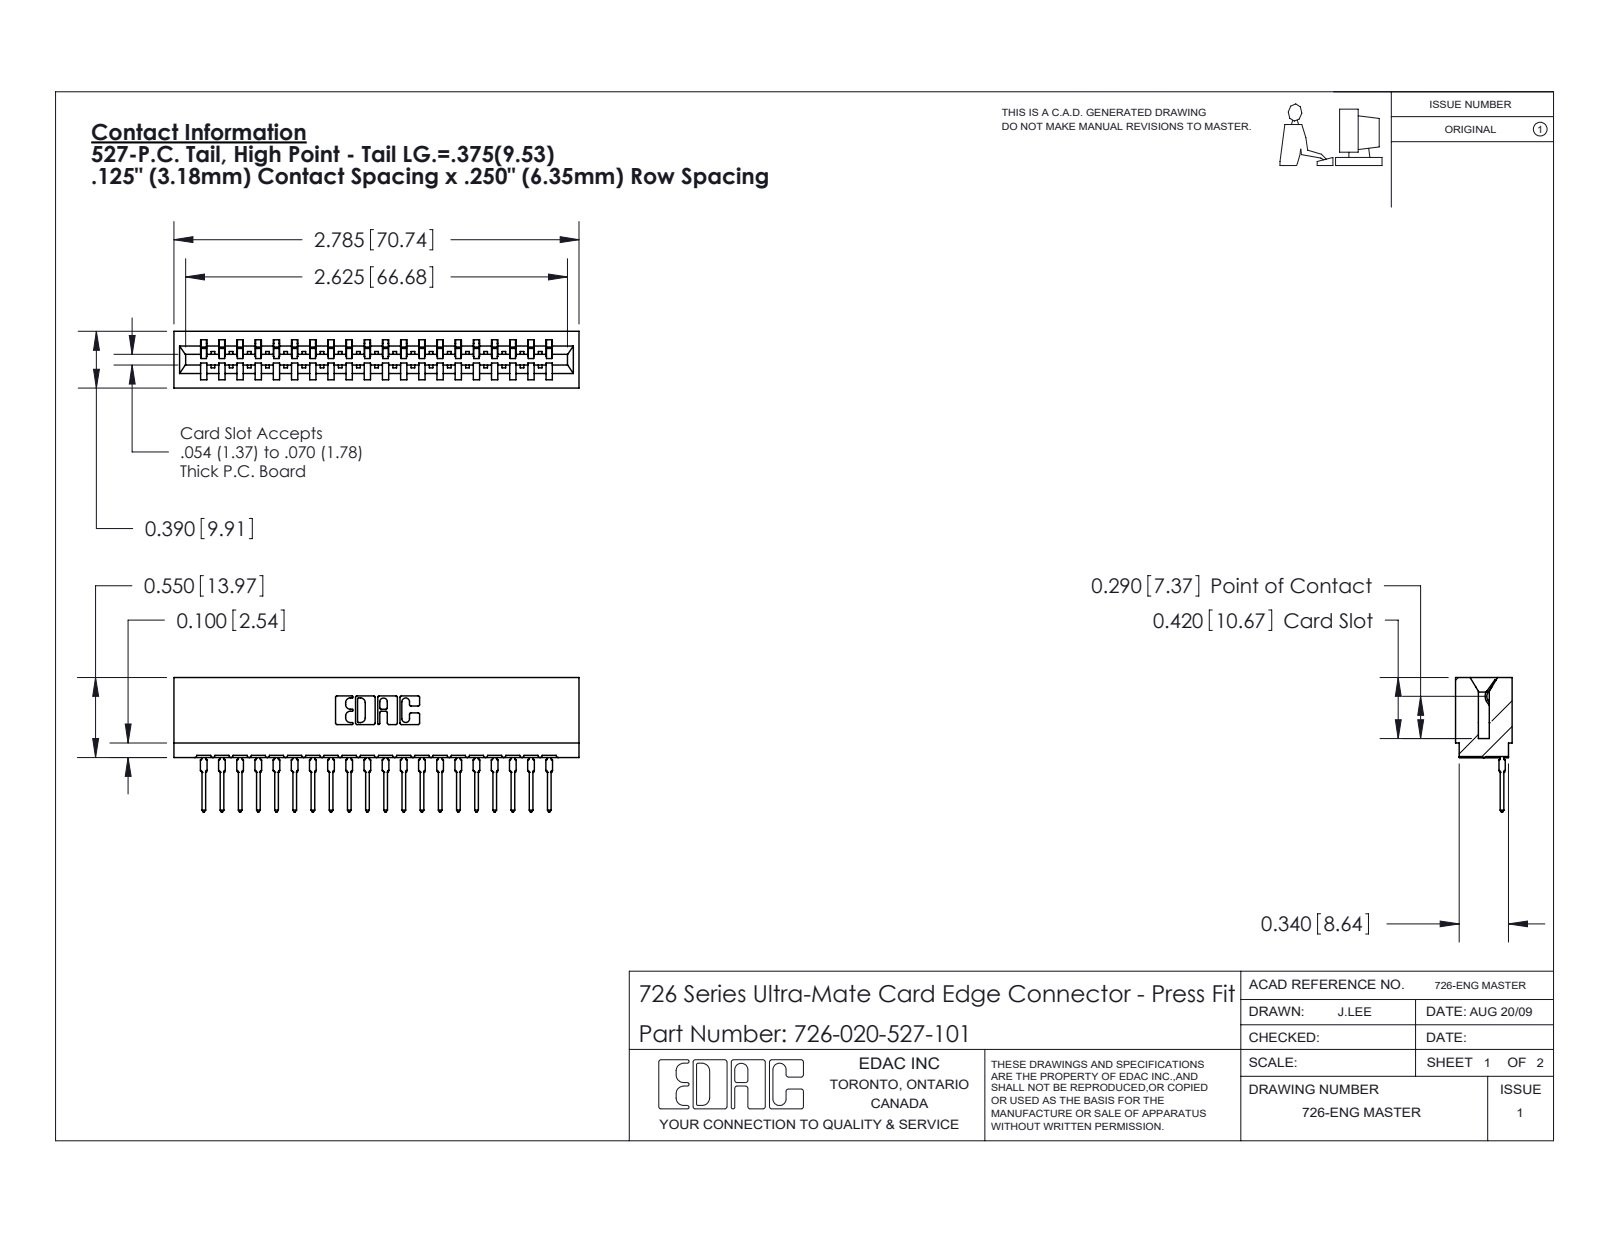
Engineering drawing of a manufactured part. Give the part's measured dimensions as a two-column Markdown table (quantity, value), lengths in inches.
| quantity | value |
| --- | --- |
| part name | 726-020-527-101; 746-292-001_527; 726 Part_.515 Slot Depth - 01 |
| STEP written by | SolidWorks 2020 (CONFIG_CONTROL_DESIGN) |
| units | inches |
| bodies | 21 solids, 2257 faces (1315 planar, 422 cylindrical, 520 other) |
| overall size | 2.785 × 0.924 × 0.39 |
| volume | 0.394 in³ |
| surface area | 14.96 in² |
| partial cylindrical surfaces (radius × count) | 0.021 × 40, 0.01 × 22, 0.015 × 21, 0.007 × 6, 0.031 × 6, 0.005 × 4, 0.011 × 4, 0.026 × 3 |
| main face-to-face distances | 0.057, 0.333, 0.25, 0.39, 0.025, 0.307, 0.5, 0.75, 0.375, 0.625 |
